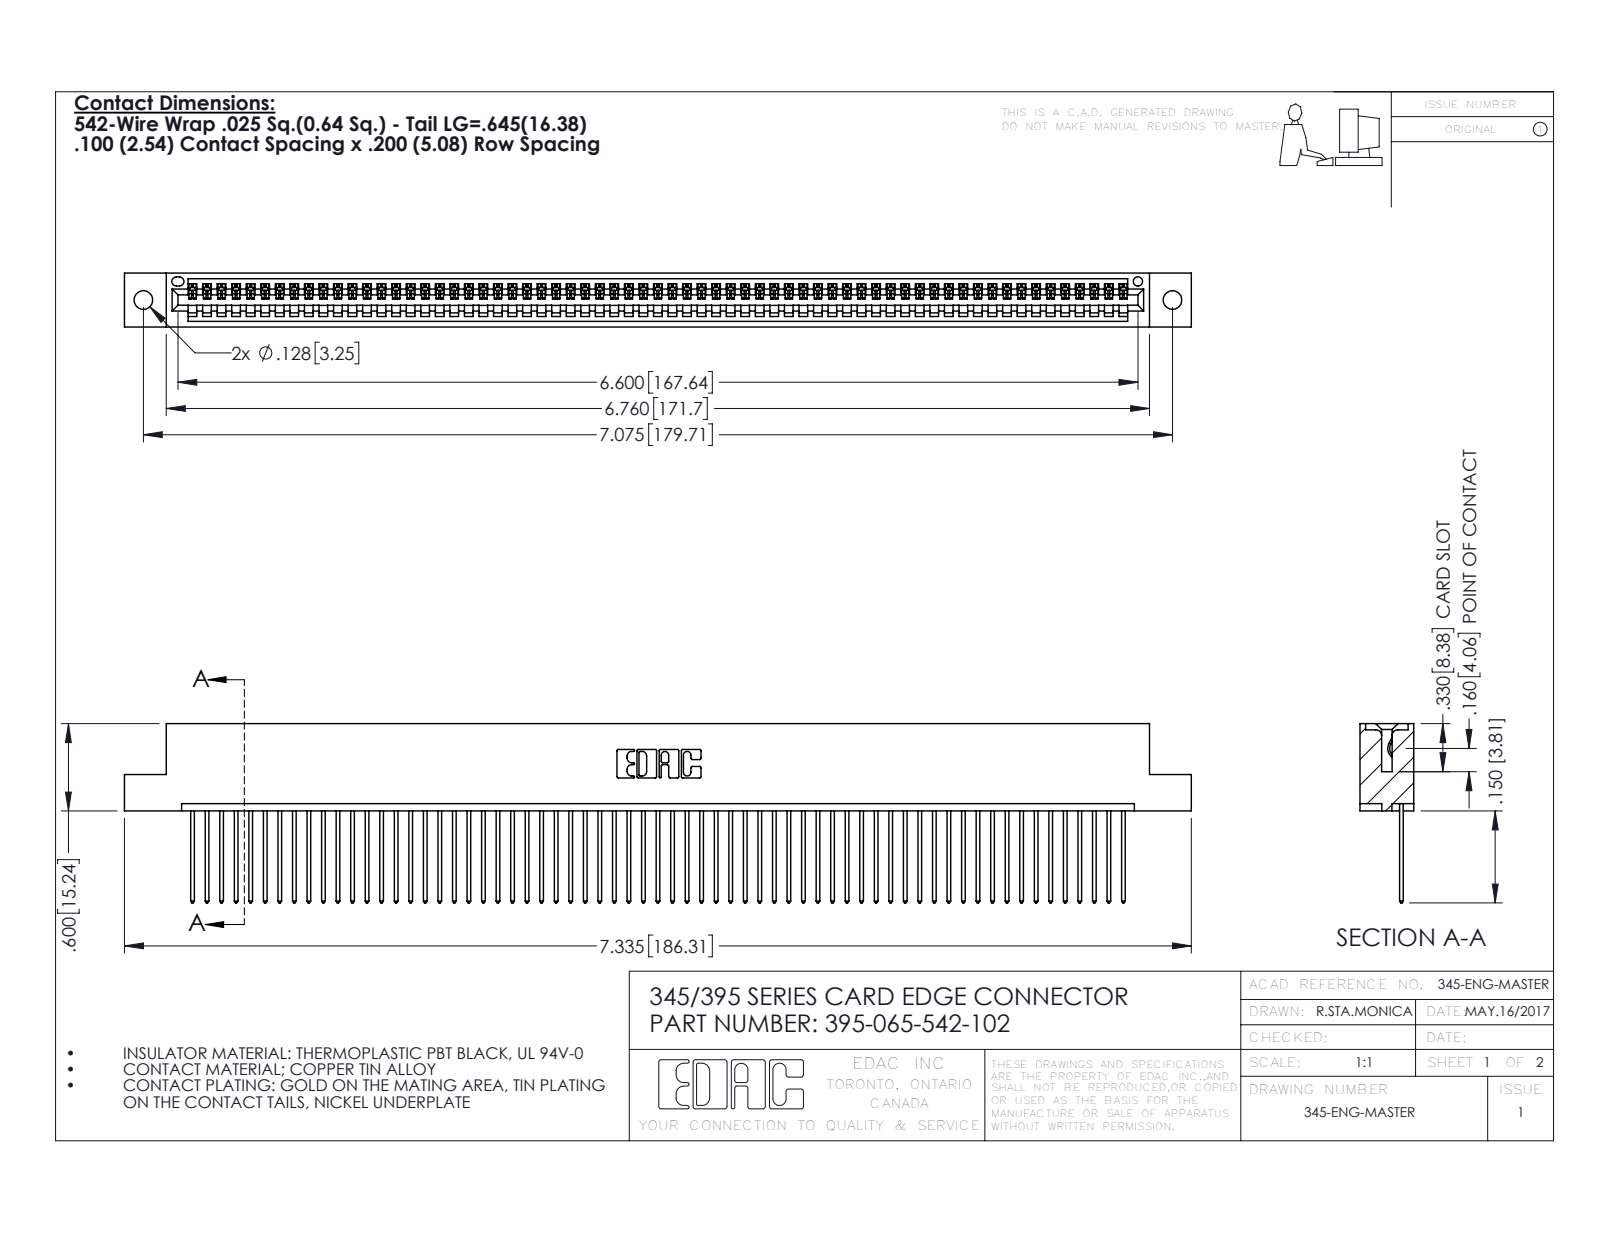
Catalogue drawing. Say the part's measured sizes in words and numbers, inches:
The part is named "395-065-542-102; 345 Part_Flush Mounting Lugs - 0.128 Dia; 345-292-001_345-293-142". Its 3-D file was written by "SolidWorks 2016 (CONFIG_CONTROL_DESIGN)". It is 66 solids with 3896 faces: 2680 planar, 1216 cylindrical and 0 other. Overall it measures 7.335 by 1.232 by 0.37 inches. Its volume is 1.098 cubic inches and its surface area 38.54 square inches. Round holes: 2 of diameter 0.128, 1 of diameter 0.064. Partial cylindrical surfaces (rounded edges, fillets, slot ends): 130 of radius 0.006, 130 of radius 0.01, 22 of radius 0.01, 6 of radius 0.007, 6 of radius 0.031, 3 of radius 0.026, 2 of radius 0.031, 2 of radius 0.04. The main face-to-face distances are 0.072, 0.298, 0.098, 0.272, 0.025, 0.37, 0.2, 0.225, 0.149, 0.072. The hole center spacings are 0.27, 6.839, 7.075.
